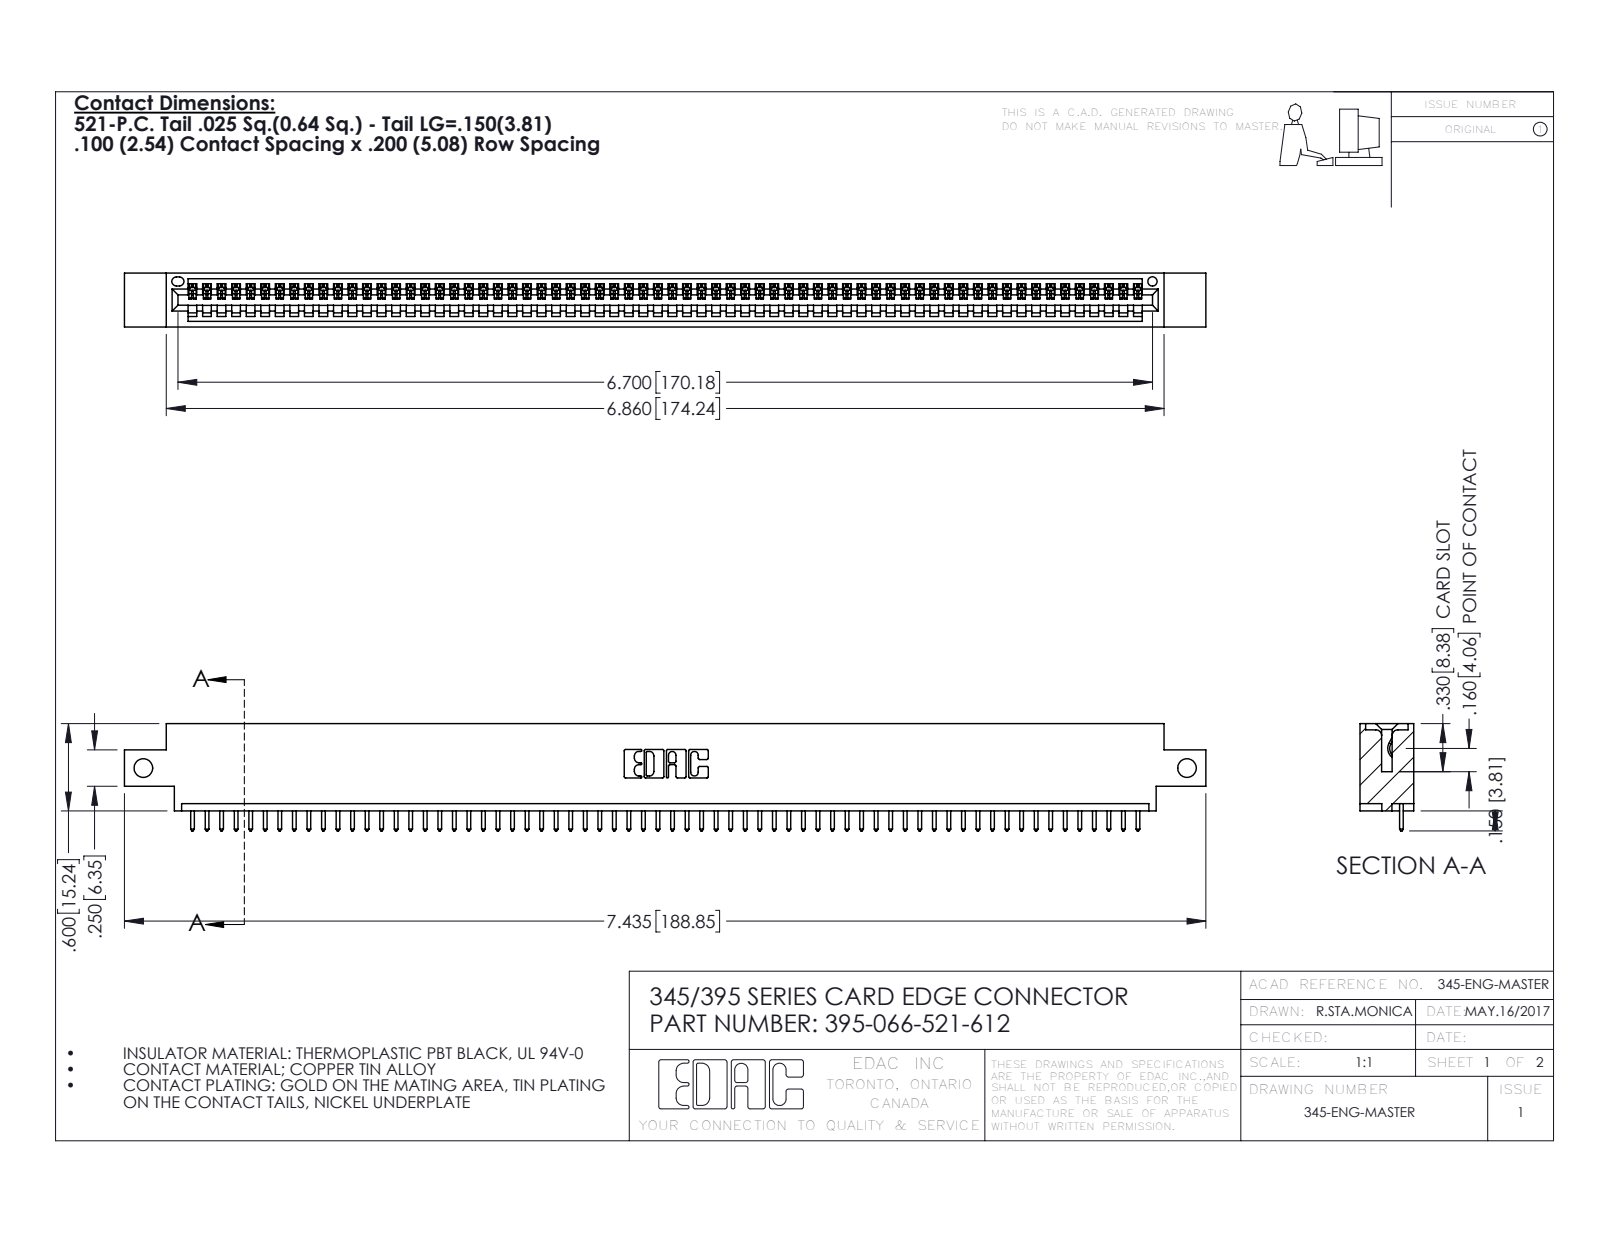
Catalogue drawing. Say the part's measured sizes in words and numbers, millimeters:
The part is named "345-292-001_345-293-121; 395-066-521-612; 345 Part_0.170 Offset - Side Mount". Its 3-D file was written by "SolidWorks 2016 (CONFIG_CONTROL_DESIGN)". It is 67 solids with 3958 faces: 2724 planar, 1234 cylindrical and 0 other. Overall it measures 188.8 by 18.7 by 9.4 millimeters. Its volume is 17 750 cubic millimeters and its surface area 23 160 square millimeters. Round holes: 2 of diameter 3.3, 1 of diameter 1.6. Partial cylindrical surfaces (rounded edges, fillets, slot ends): 132 of radius 0.2, 132 of radius 0.3, 22 of radius 0.3, 6 of radius 0.2, 6 of radius 0.8, 3 of radius 0.7, 2 of radius 0.8, 2 of radius 1. The main face-to-face distances are 7.6, 1.8, 9.4, 5.1, 2.5, 6.9, 0.6, 5.7, 4.4, 3.8. The hole center spacings are 182.2.
